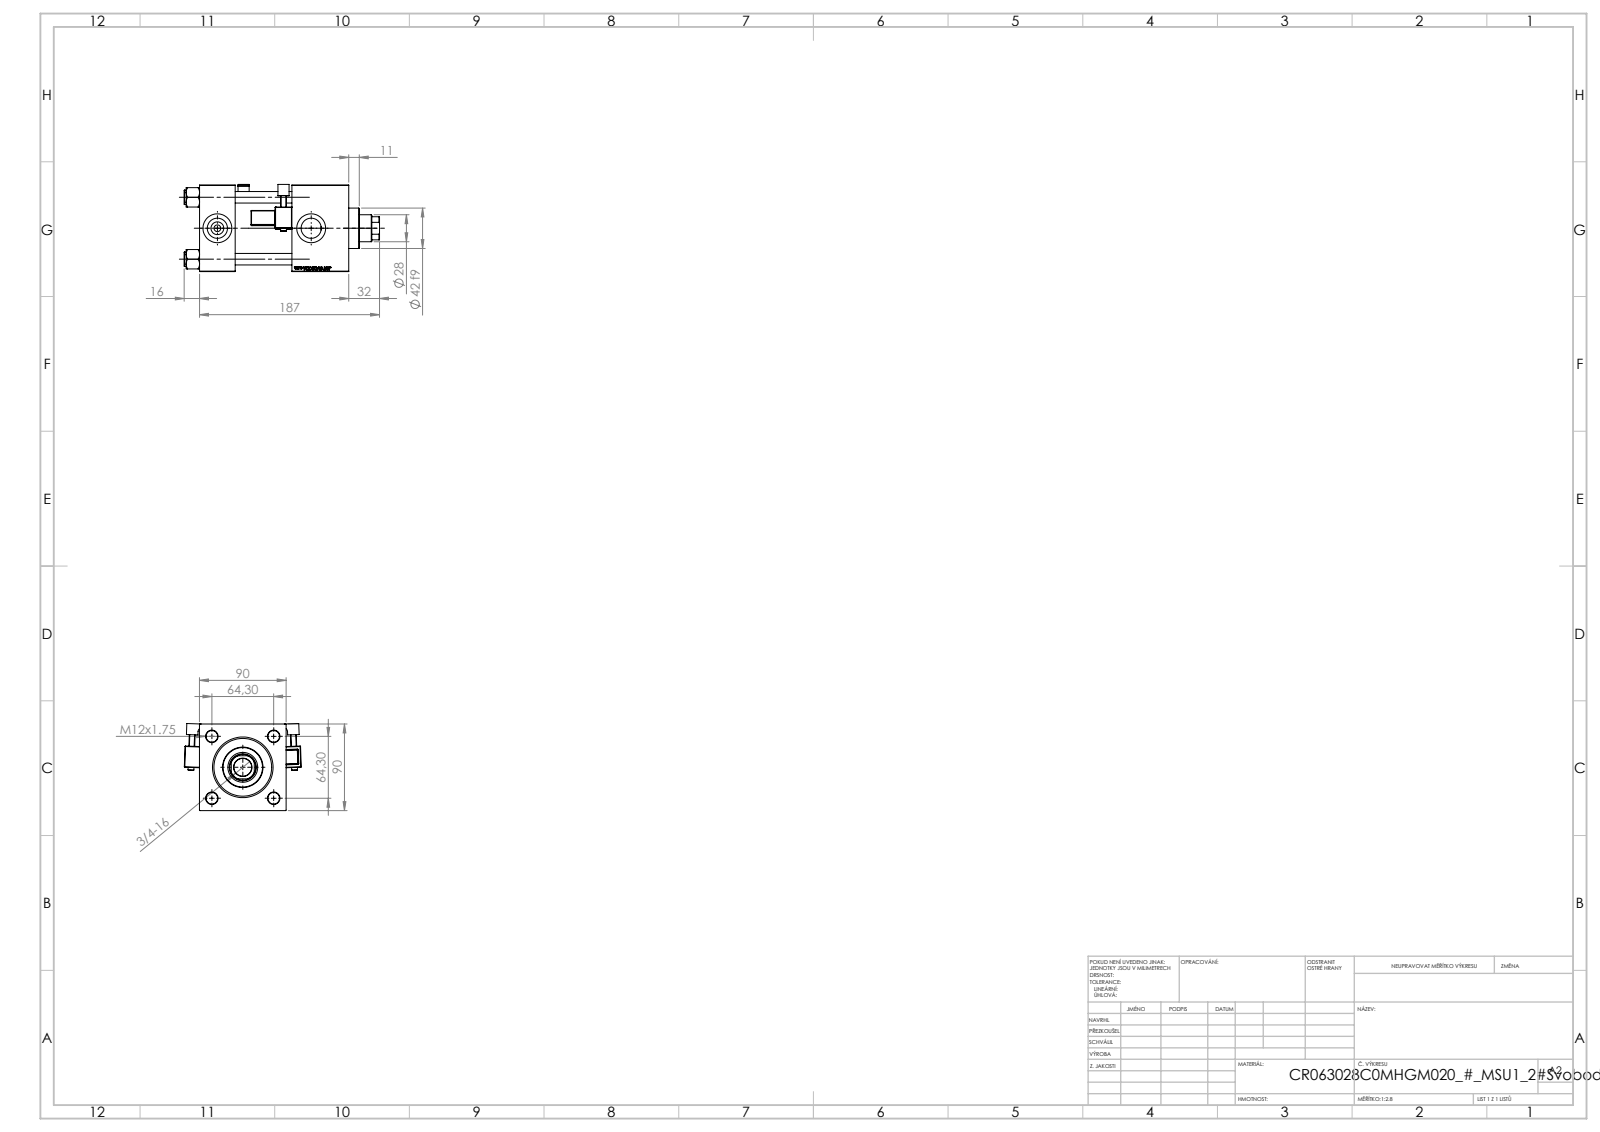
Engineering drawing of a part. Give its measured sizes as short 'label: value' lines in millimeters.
name: V215CR_C_Body; V215CR_MSU; V215CR_VCP_C; V215_VC_A (+2 more)
written by: SolidWorks 2019 (CONFIG_CONTROL_DESIGN)
unit: mm
bodies: 13 solids, 1302 faces (584 planar, 146 cylindrical, 572 other)
size: 203 × 121.57 × 90.53
volume: 988 032 mm³; area: 191 397 mm²
holes: 4× ⌀12, 2× ⌀7, 2× ⌀20.96, 2× ⌀30, 1× ⌀18.5, 1× ⌀28, 1× ⌀31, 1× ⌀50, 1× ⌀60, 1× ⌀63
bosses: 4× ⌀15, 2× ⌀6, 1× ⌀69, 1× ⌀42
rounds: 48× R0.5, 2× R1, 2× R2.5, 2× R4, 1× R13.5
face distances: 90, 59, 37, 155, 118, 96, 126.3, 89.3, 30.3, 28.7
hole spacings: 45.47, 64.3, 90.93, 97.5
